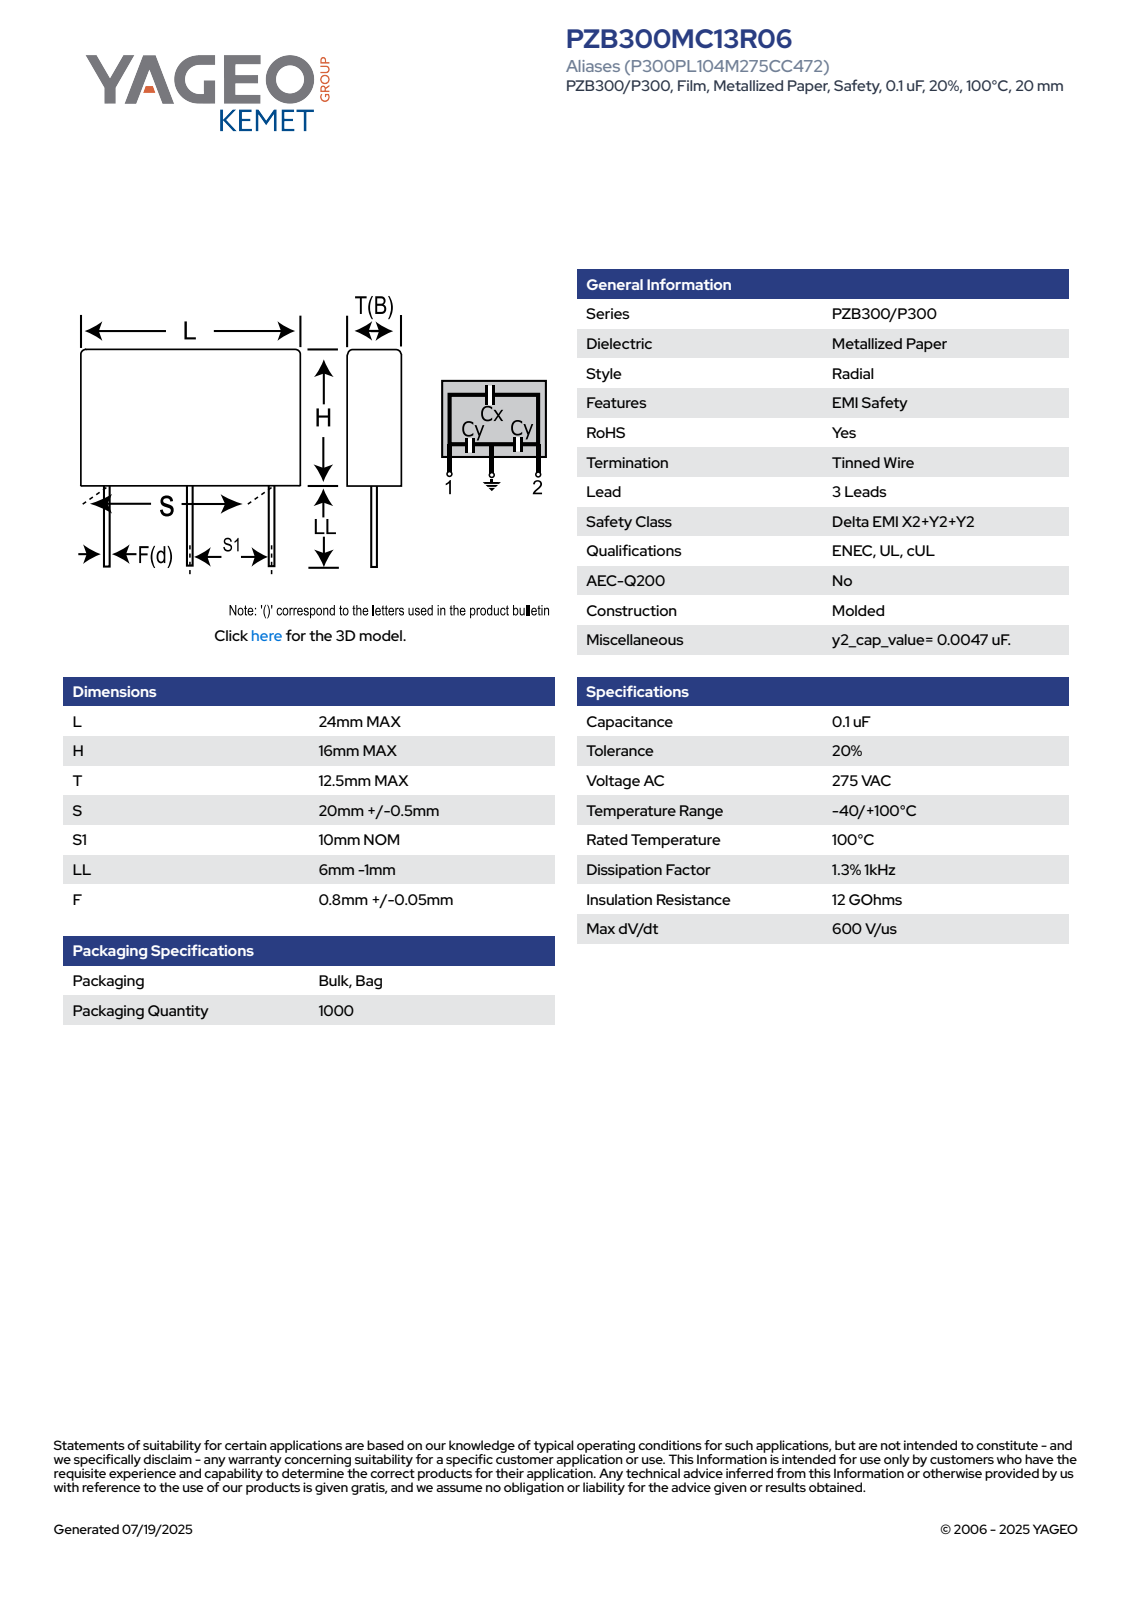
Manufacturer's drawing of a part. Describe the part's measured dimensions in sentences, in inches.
The part is named "CFR_PZB300_24X16X12.5L24H16T12.5S20S110LL5F0.85". Its 3-D file was written by "SolidWorks 2014 (AUTOMOTIVE_DESIGN)". It is 4 solids with 76 faces: 66 planar, 10 cylindrical and 0 other. Overall it measures 0.945 by 0.827 by 0.493 inches. Its volume is 0.293 cubic inches and its surface area 2.827 square inches. Round bosses or shafts: 3 of diameter 0.033. Partial cylindrical surfaces (rounded edges, fillets, slot ends): 4 of radius 0.024. The main face-to-face distances are 0.492, 0.63, 0.945, 0.493, 0.197, 0.827, 0.268, 0.559, 0.362, 0.463.
